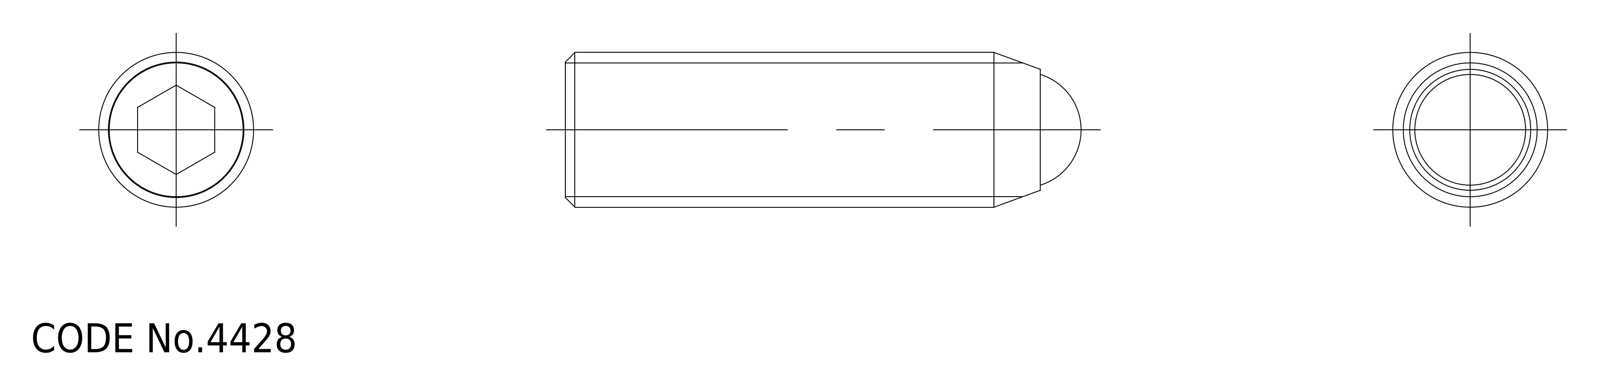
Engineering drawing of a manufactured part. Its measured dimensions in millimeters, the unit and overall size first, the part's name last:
Units: millimetres
Overall size (bounding box): 53.3 × 16 × 16
Volume: 8 989 mm³ · Surface area: 3 833 mm²
Bodies: 2 solids, 20 faces (0 planar, 0 cylindrical, 20 other)
Part name (STEP PRODUCT): ball; SCSS_M16_50_R_18626_36
STEP written by: CADfix (AUTOMOTIVE_DESIGN)
